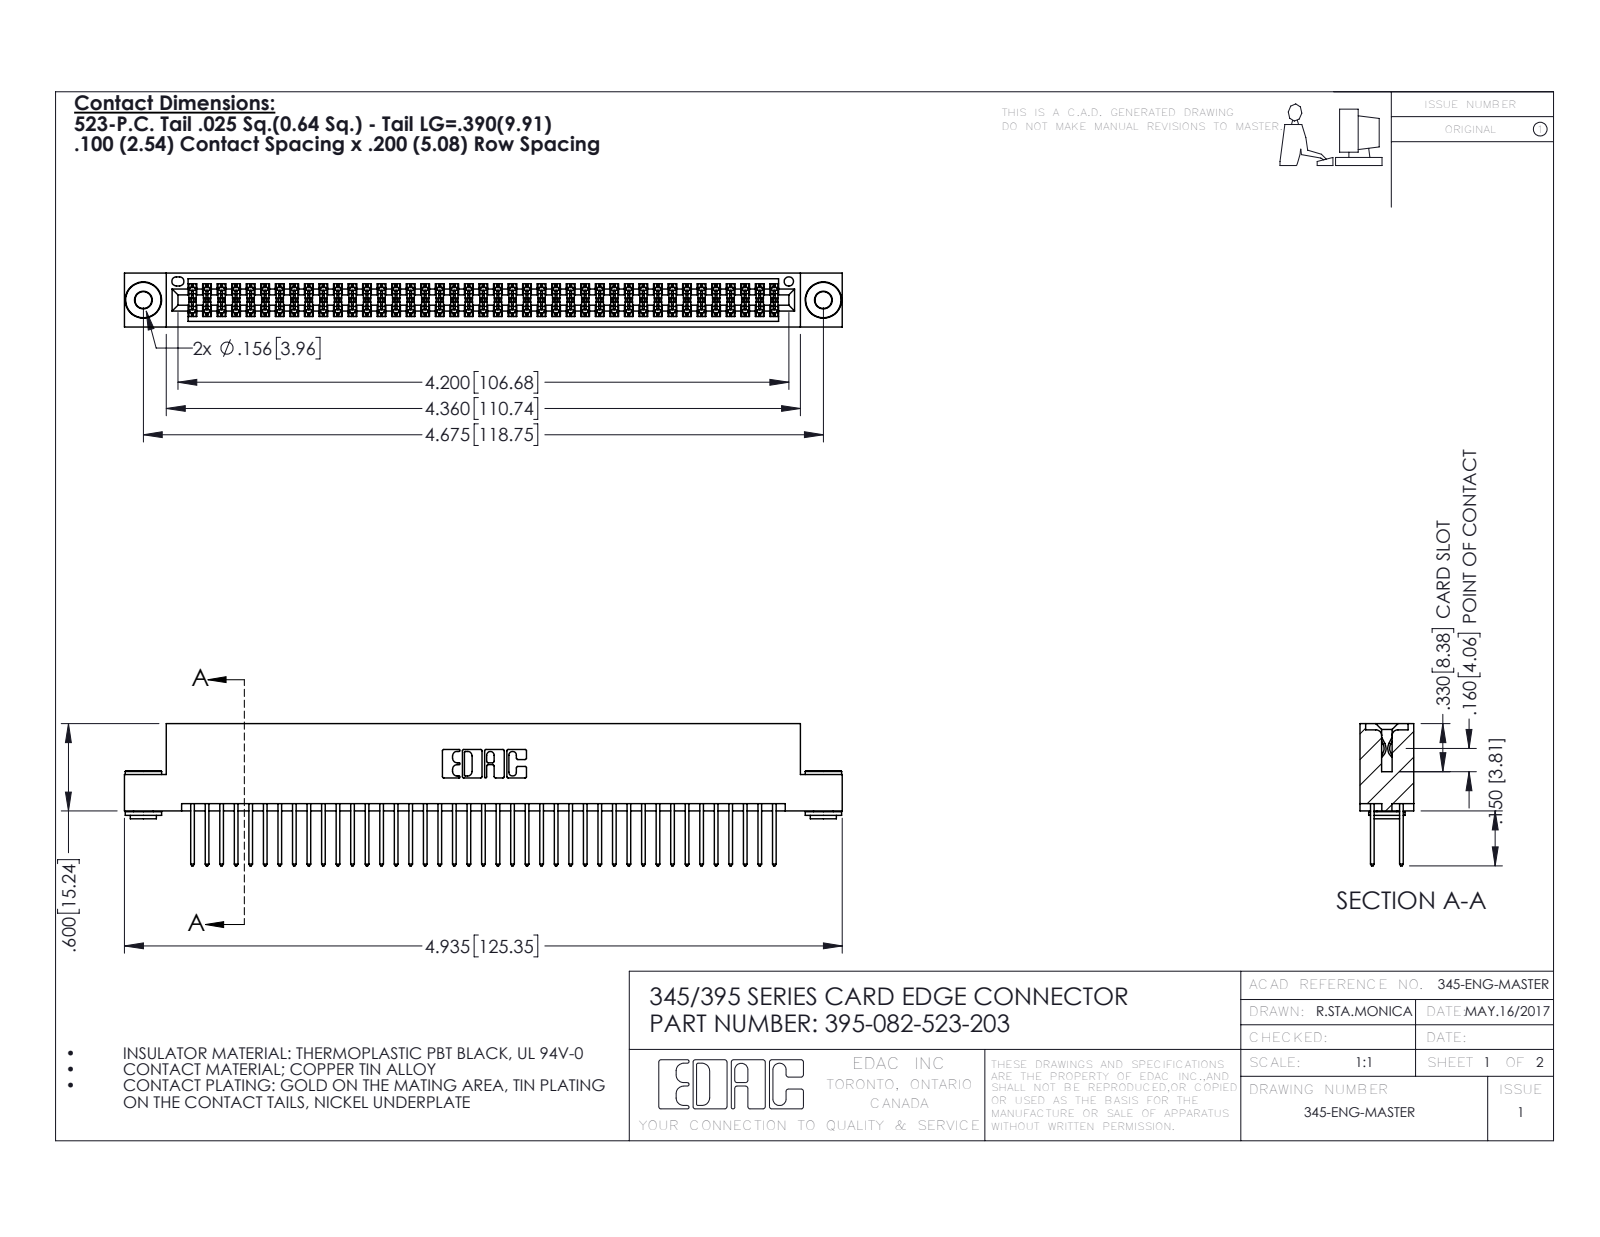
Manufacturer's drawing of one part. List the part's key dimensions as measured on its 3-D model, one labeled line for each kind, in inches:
Part name (STEP PRODUCT): 345-250-002_345-250-002-102; 345-292-001_345-293-123; 395-082-523-203; 345 Part_Flush Mounting Lugs - 0.156 Dia-TH
STEP written by: SolidWorks 2016 (CONFIG_CONTROL_DESIGN)
Units: inches
Bodies: 85 solids, 4264 faces (2796 planar, 1460 cylindrical, 8 other)
Overall size (bounding box): 4.935 × 0.977 × 0.37
Volume: 0.754 in³ · Surface area: 29.76 in²
Round holes (diameter × count): ⌀0.116 ×2, ⌀0.156 ×2, ⌀0.064 ×1
Round bosses / shafts (diameter × count): ⌀0.25 ×2, ⌀0.18 ×2, ⌀0.136 ×2
Partial cylindrical surfaces — rounded edges, fillets, slot ends (radius × count): R0.006 ×123, R0.01 ×82, R0.01 ×22, R0.007 ×6, R0.031 ×6, R0.026 ×3, R0.014 ×2, R0.019 ×2
Main face-to-face distances: 0.072, 0.298, 0.2, 0.025, 0.098, 0.272, 0.37, 0.225, 0.175, 0.149
Hole centre spacings: 0.27, 4.439, 4.675
